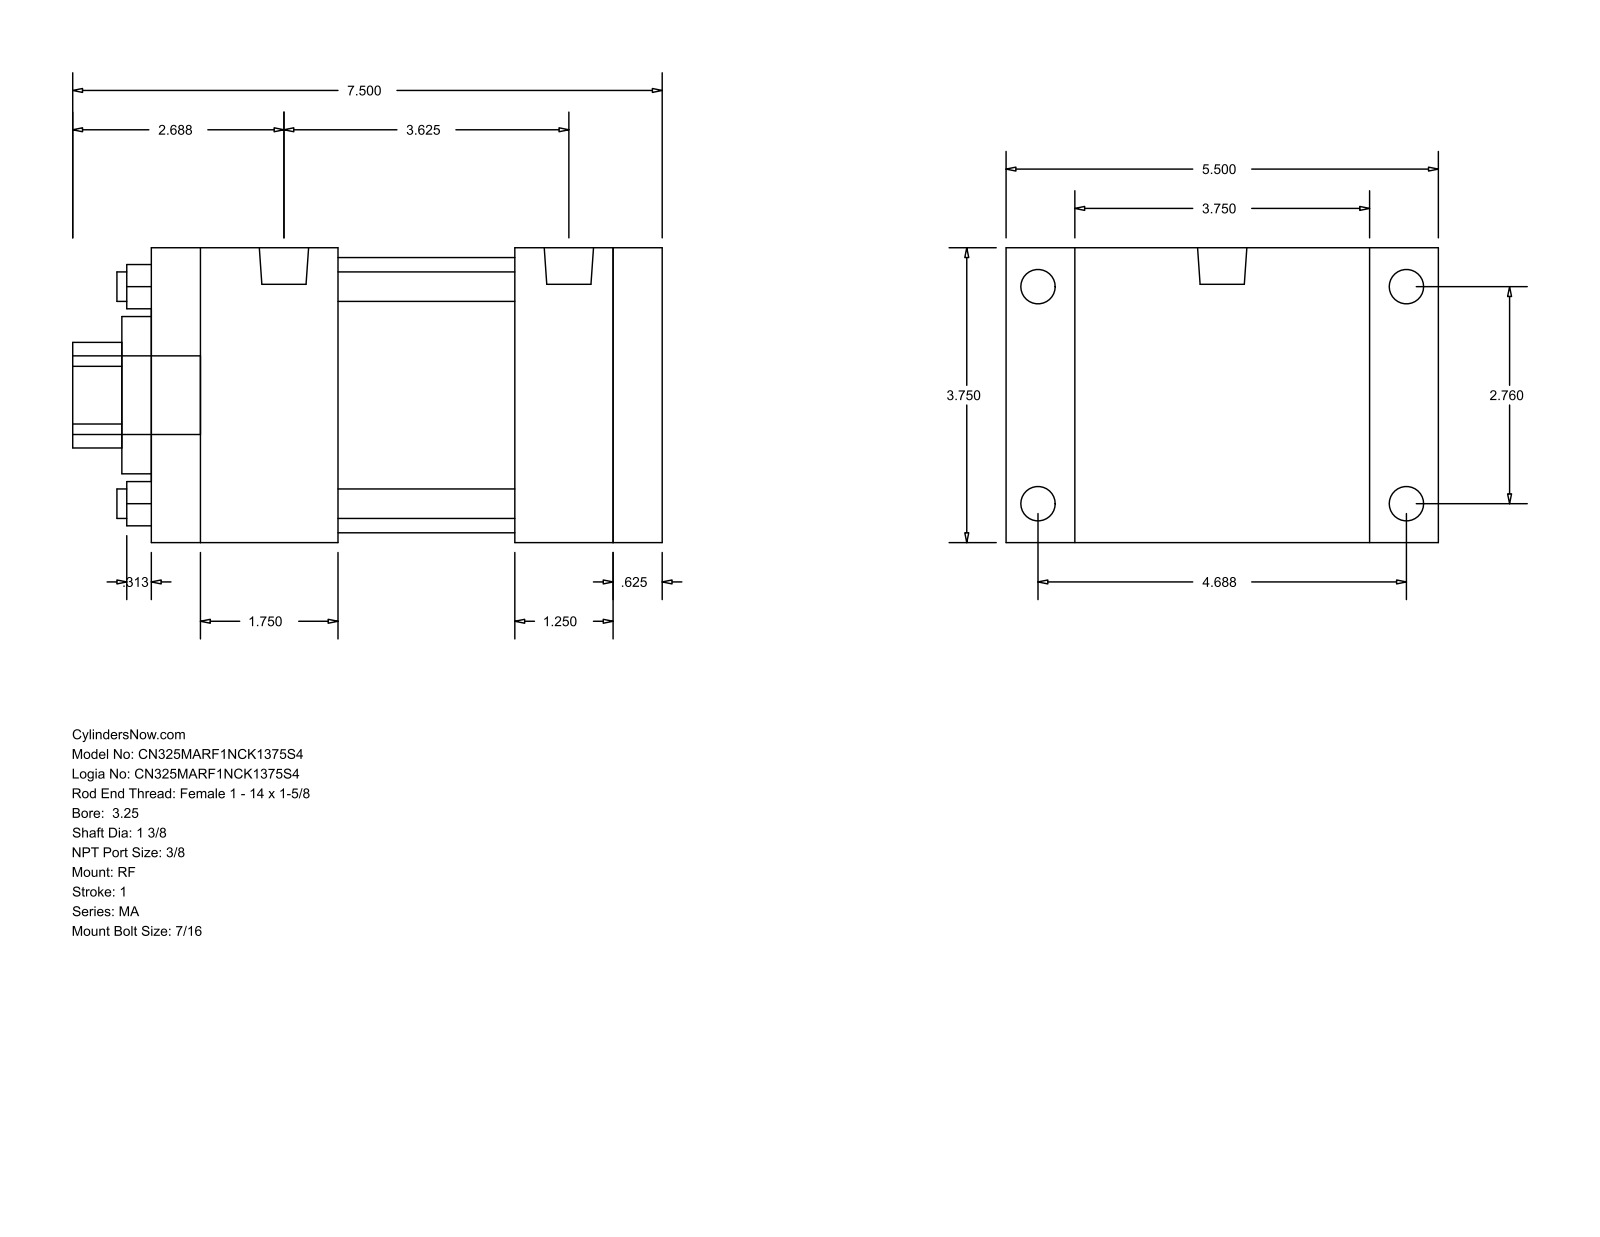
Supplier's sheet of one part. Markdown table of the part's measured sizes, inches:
| quantity | value |
| --- | --- |
| part name | MA_RF__0325_1.375 |
| STEP written by | GSSL Pune (CONFIG_CONTROL_DESIGN) |
| units | inches |
| bodies | 0 solids, 92 faces (64 planar, 28 cylindrical, 0 other) |
| overall size | 7.5 × 5.5 × 3.75 |
| round holes (diameter × count) | 0.375 × 4, 1.375 × 1, 2 × 1, 3.5 × 1 |
| round bosses / shafts (diameter × count) | 0.437 × 8, 0.627 × 2, 1 × 1 |
| partial cylindrical surfaces (radius × count) | 0.672 × 1 |
| main face-to-face distances | 3.75, 6.5, 0.625, 5.875, 0.875, 4.625, 4.625, 1.25, 1.875, 2.375 |
| hole center spacings | 1.952, 2.76, 3.903 |
